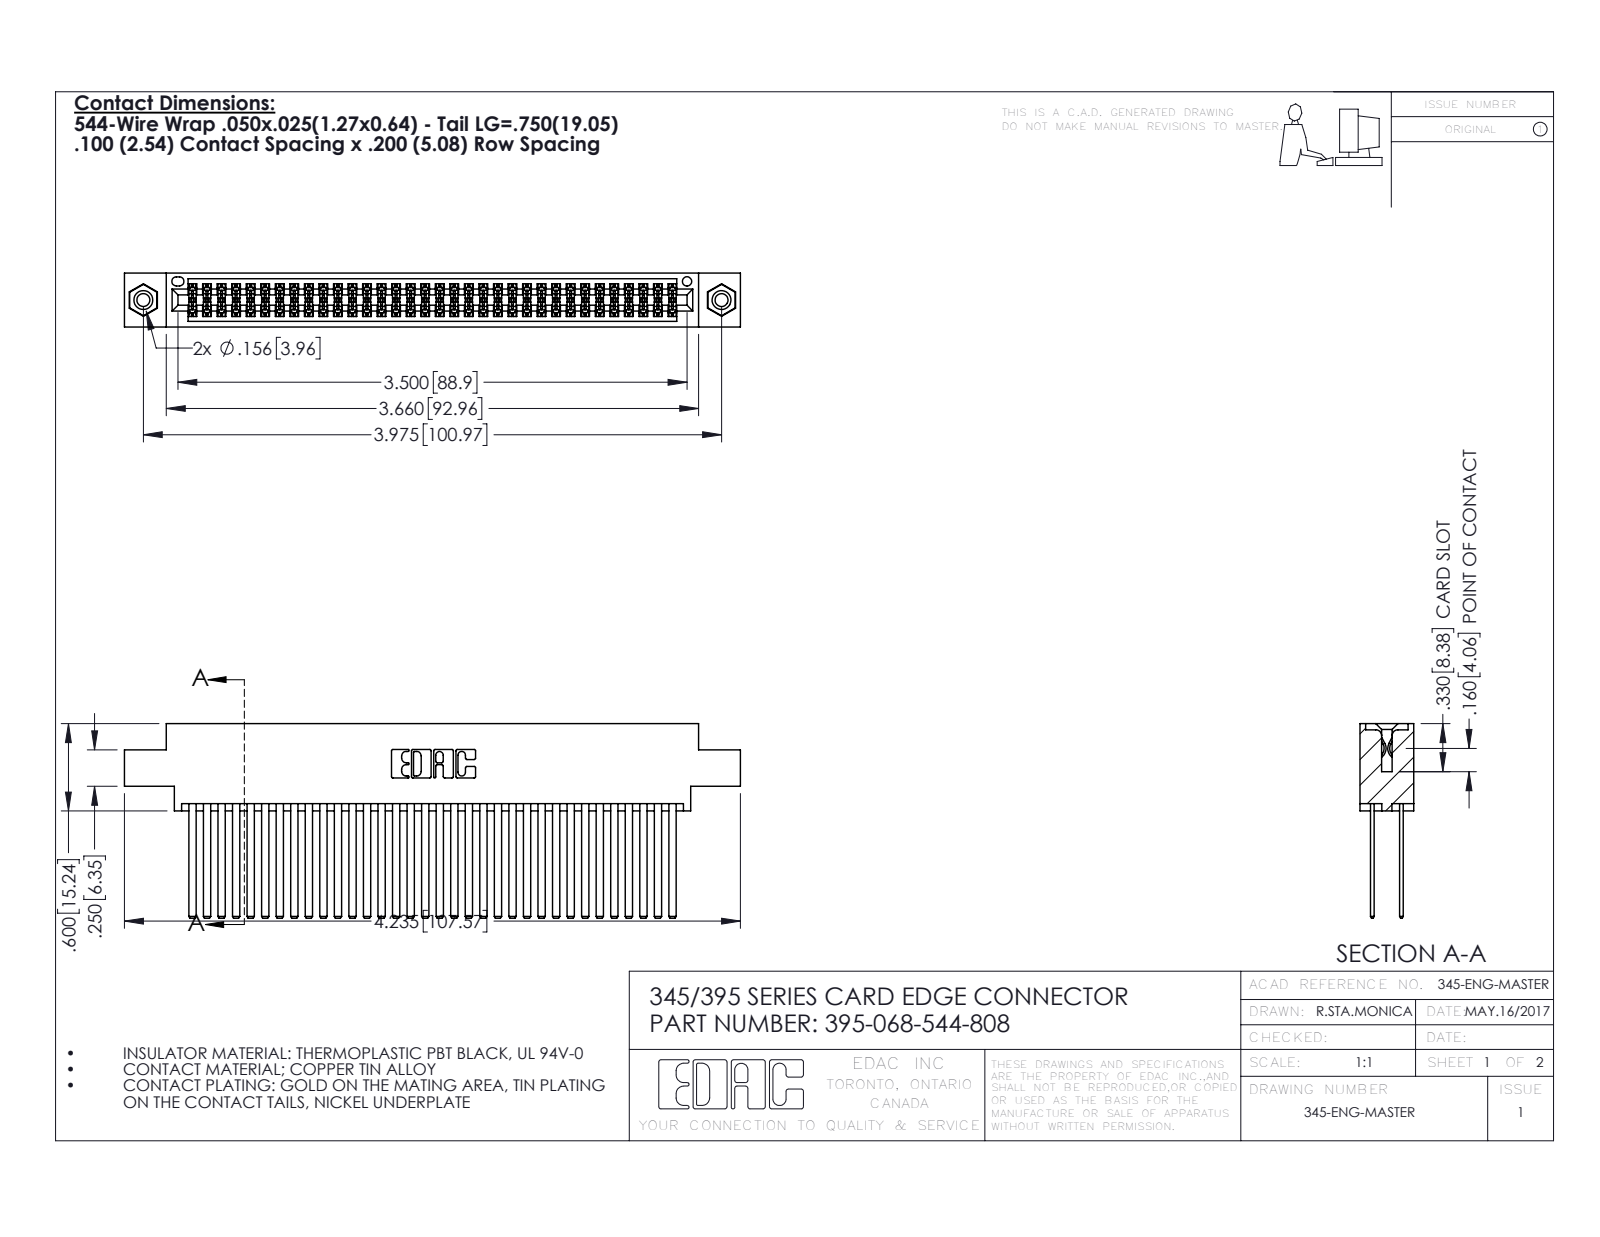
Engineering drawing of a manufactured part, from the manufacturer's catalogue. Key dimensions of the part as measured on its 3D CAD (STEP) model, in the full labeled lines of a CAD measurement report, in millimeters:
Part name (STEP PRODUCT): 345-292-001_345-293-144; 395-068-544-808; 345-250-001_345-250-003-102; 345 Part_0.170 Offset - 0.156 Dia-TI
STEP written by: SolidWorks 2016 (CONFIG_CONTROL_DESIGN)
Units: millimetres
Bodies: 71 solids, 3182 faces (2088 planar, 1078 cylindrical, 16 other)
Overall size (bounding box): 107.6 × 34 × 9.4
Volume: 11 200 mm³ · Surface area: 19 360 mm²
Round holes (diameter × count): ⌀2.3 ×2, ⌀3.2 ×2, ⌀4 ×2, ⌀1.6 ×1
Round bosses / shafts (diameter × count): ⌀3.9 ×2
Partial cylindrical surfaces — rounded edges, fillets, slot ends (radius × count): R0.2 ×102, R0.3 ×22, R0.2 ×6, R0.8 ×6, R0.7 ×3, R0.4 ×2, R0.5 ×2, R0.6 ×2
Main face-to-face distances: 5.1, 0.6, 1.8, 2.5, 6.9, 7.6, 5.7, 4.4, 9.4, 3.8
Hole centre spacings: 6.9, 95, 101
